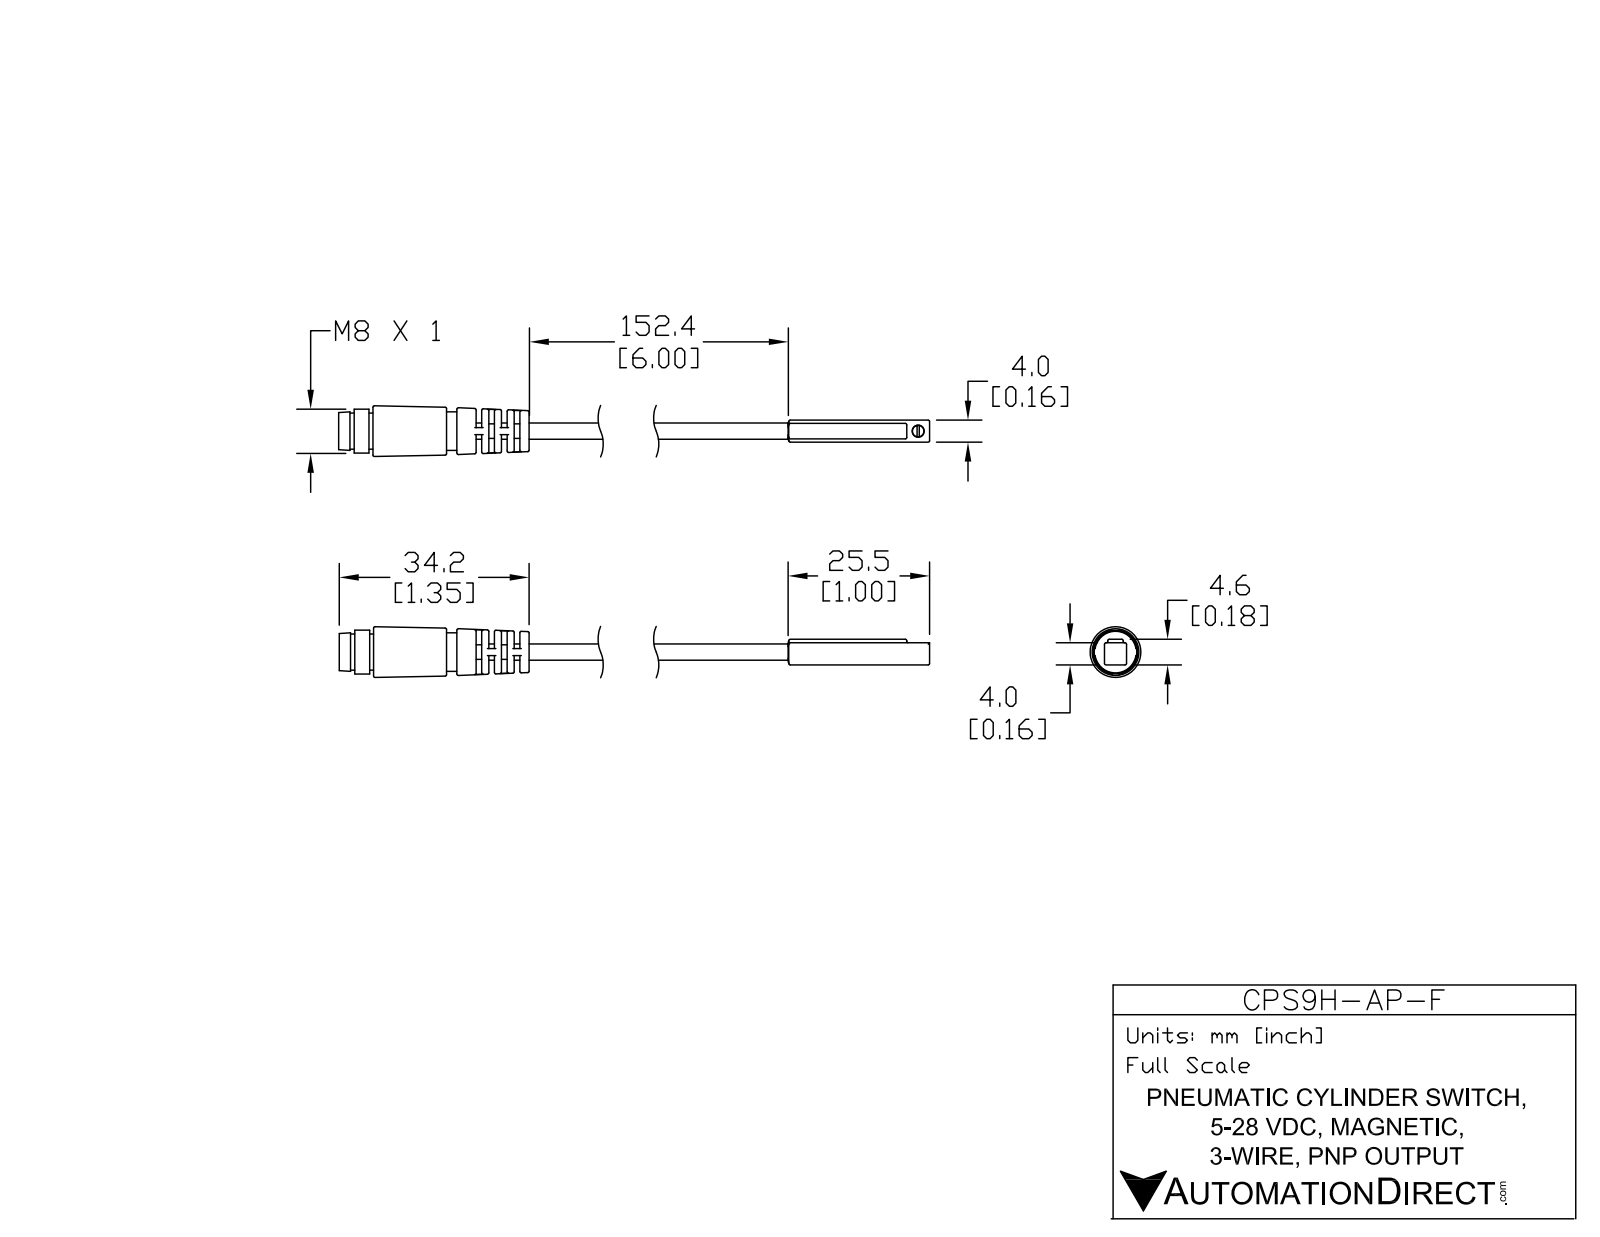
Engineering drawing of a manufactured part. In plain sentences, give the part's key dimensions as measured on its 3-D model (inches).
The part is named "CPS9H-AP-F; 9H72-000-331.igs1_1; 9H72-000-331.igs2_1". Its 3-D file was written by "SolidWorks 2014 (AUTOMOTIVE_DESIGN)". It is 2 solids with 185 faces: 56 planar, 55 cylindrical and 74 other. Overall it measures 7.125 by 0.36 by 0.36 inches. Its volume is 0.169 cubic inches and its surface area 4.653 square inches. Round holes: 1 of diameter 0.086, 1 of diameter 0.227. Round bosses or shafts: 3 of diameter 0.04, 1 of diameter 0.311, 1 of diameter 0.273, 1 of diameter 0.256, 1 of diameter 0.115, 1 of diameter 0.082. Partial cylindrical surfaces (rounded edges, fillets, slot ends): 22 of radius 0.01, 1 of radius 0.058. The main face-to-face distances are 0.09, 0.156, 0.05, 0.04, 0.18, 0.09, 0.22, 0.13, 0.27, 0.182.
